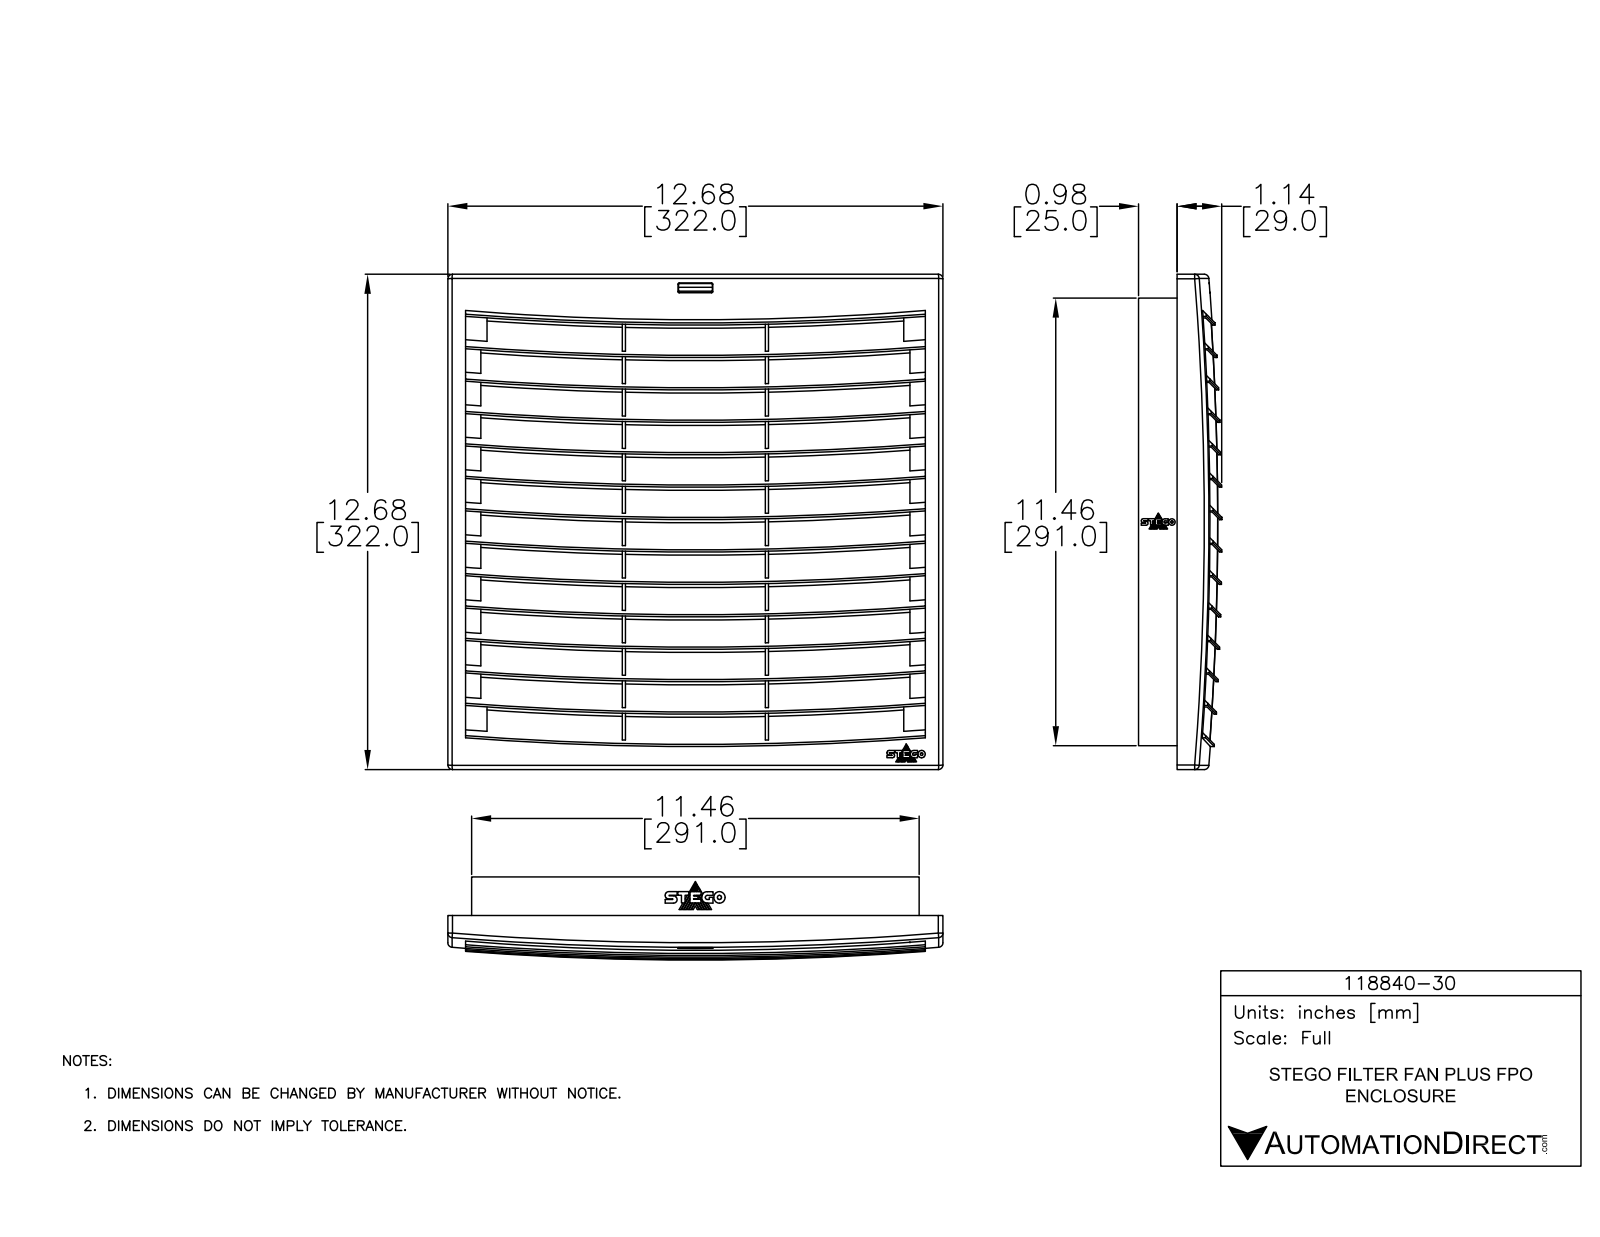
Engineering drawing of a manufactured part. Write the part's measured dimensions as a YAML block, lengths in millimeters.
part_name: "118840-30"
step_written_by: "SolidWorks 2018 (AUTOMOTIVE_DESIGN)"
units: millimeters
bodies: {solids: 1, faces: 565, planar: 301, cylindrical: 264, other: 0}
overall_size: [322, 322, 54]
volume: 1652000
surface_area: 598500
round_holes:
  - {diameter: 119.2, count: 1}
  - {diameter: 150.1, count: 1}
  - {diameter: 181, count: 1}
  - {diameter: 211.9, count: 1}
  - {diameter: 247.3, count: 1}
round_bosses_or_shafts:
  - {diameter: 220.9, count: 1}
  - {diameter: 190, count: 1}
  - {diameter: 159.1, count: 1}
  - {diameter: 128.2, count: 1}
partial_cylinders:
  - {radius: 1650, count: 23}
  - {radius: 7, count: 4}
  - {radius: 30.9, count: 1}
  - {radius: 44.1, count: 1}
  - {radius: 48.6, count: 1}
  - {radius: 1123.1, count: 1}
face_to_face_distances: [16.2, 32.3, 48.5, 7.5, 64.6, 80.8, 1.5, 25, 17.5, 17.7]
